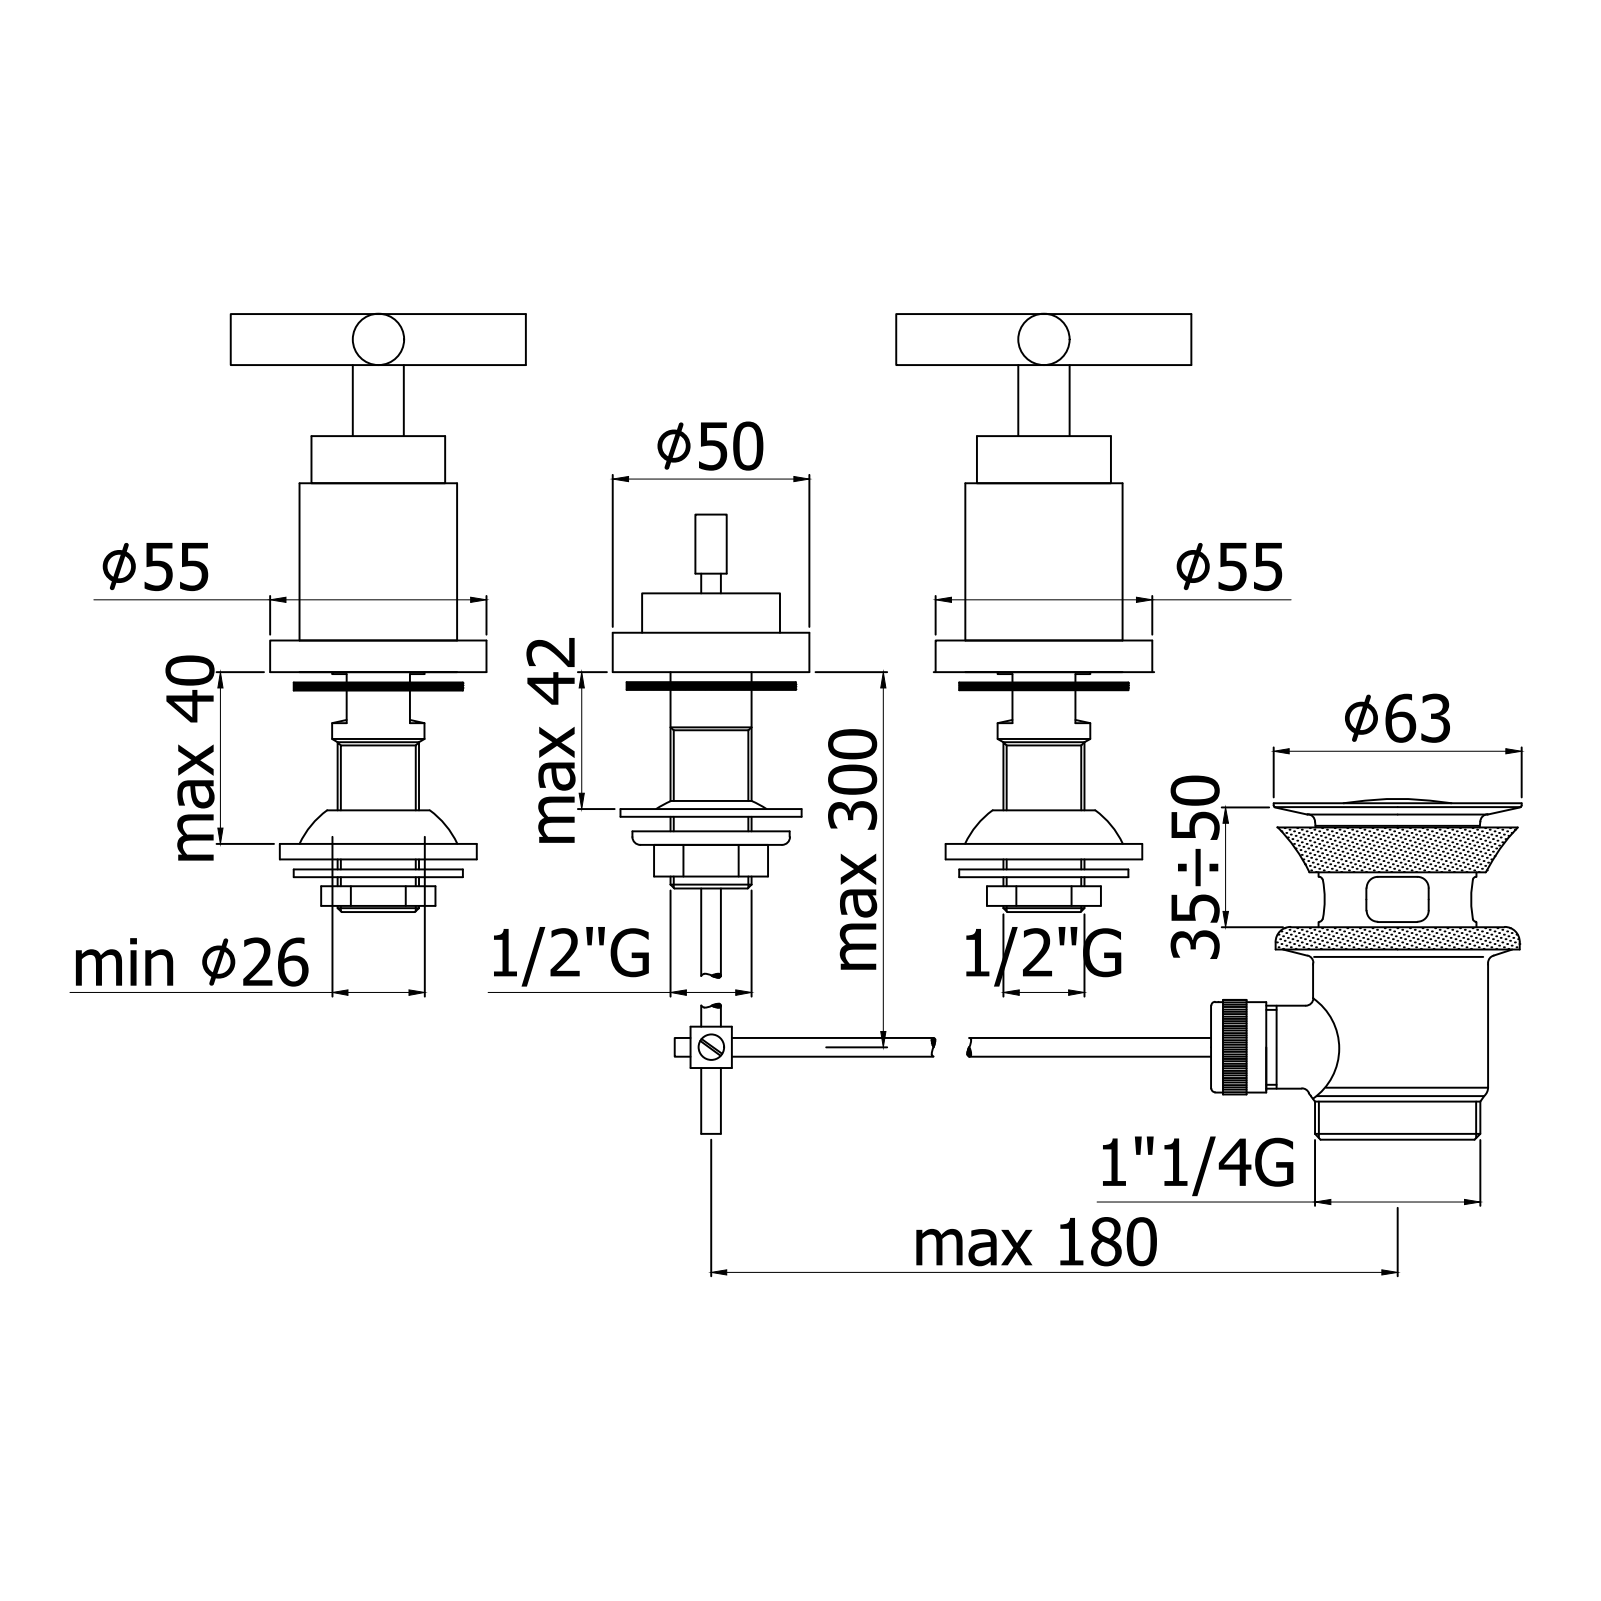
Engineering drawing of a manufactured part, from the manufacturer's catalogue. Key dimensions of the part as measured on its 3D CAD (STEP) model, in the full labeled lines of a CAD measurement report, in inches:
Part name (STEP PRODUCT): QTV116CR
STEP written by: CREO PARAMETRIC BY PTC INC, 2020044 (CONFIG_CONTROL_DESIGN)
Units: inches
Bodies: 7 solids, 840 faces (396 planar, 240 cylindrical, 204 other)
Overall size (bounding box): 8.858 × 2.953 × 2.705
Volume: 10.5 in³ · Surface area: 105.7 in²
Round holes (diameter × count): ⌀0.13 ×3, ⌀0.177 ×3, ⌀0.276 ×3, ⌀0.315 ×2, ⌀0.346 ×2, ⌀0.374 ×2, ⌀0.531 ×2, ⌀0.732 ×2, ⌀0.748 ×2, ⌀0.787 ×2, ⌀0.866 ×2, ⌀1.012 ×2
Round bosses / shafts (diameter × count): ⌀0.472 ×3, ⌀2.165 ×2, ⌀1.929 ×2, ⌀1.685 ×2, ⌀1.567 ×2, ⌀1.339 ×2, ⌀0.945 ×2, ⌀0.843 ×2
Partial cylindrical surfaces — rounded edges, fillets, slot ends (radius × count): R0.004 ×34, R0.02 ×20, R0.039 ×4, R0.118 ×2, R0.37 ×2, R0.512 ×2
Main face-to-face distances: 0.039, 0.394, 0.118, 0.157, 0.276, 0.236, 0.433, 0.354, 0.197, 0.748
Hole centre spacings: 2.953, 5.906
